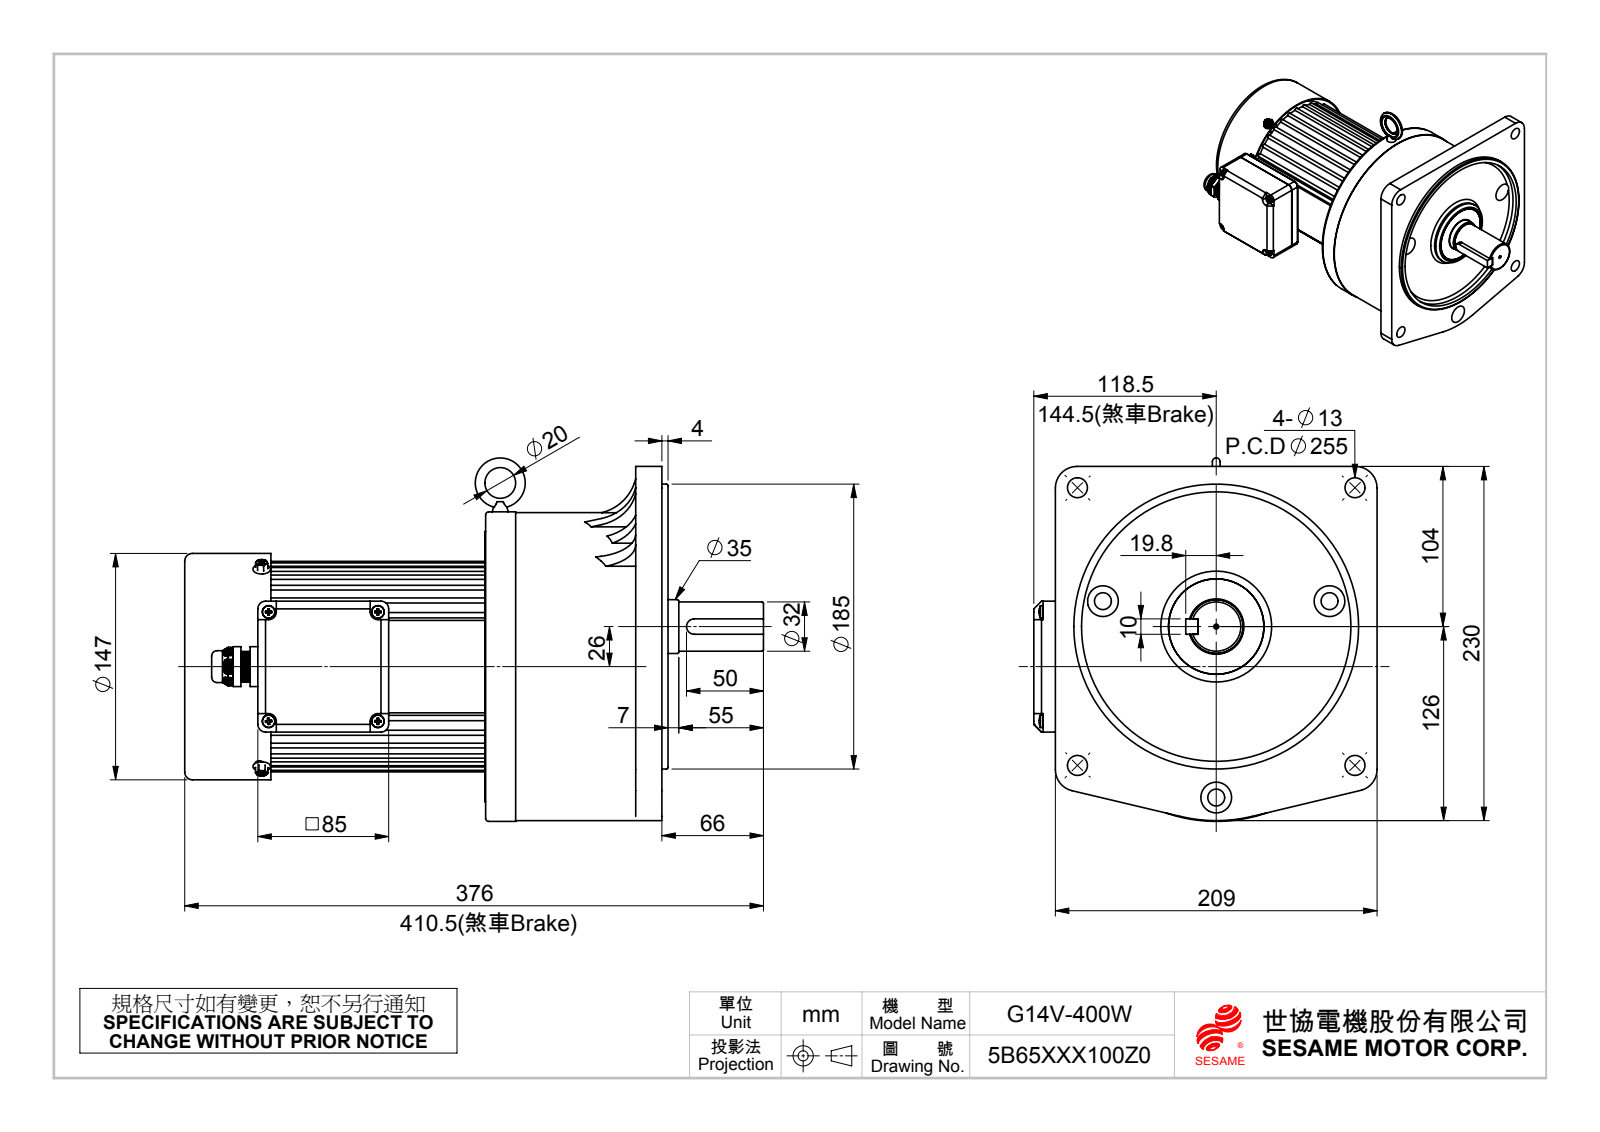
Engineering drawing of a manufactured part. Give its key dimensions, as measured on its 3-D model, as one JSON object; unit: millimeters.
{"part_name": "(標準品)G14V400W(5B65XXX100)(減速比共用); 出線盒下蓋; G14-400C1-03; 油封35x62x8 (+8 more)", "step_written_by": "SolidWorks 2010 (CONFIG_CONTROL_DESIGN)", "units": "millimeters", "bodies": {"solids": 20, "faces": 2705, "planar": 842, "cylindrical": 840, "other": 1023}, "overall_size": [376, 236, 223], "volume_mm3": 6473000, "surface_area_mm2": 567660, "round_holes": [[5, 14], [3.3, 9], [6, 5], [8, 4], [13, 4], [20, 4], [11, 3], [15, 3], [2, 1], [6.8, 1], [10.8, 1], [16.5, 1]], "round_bosses_or_shafts": [[8.3, 4], [4, 4], [5, 2], [201, 1], [200, 1], [185, 1], [175.47, 1], [147, 1]], "partial_cylinders_radius": [[1.85, 31], [1, 26], [0.5, 24], [3, 18], [5, 9], [30, 7], [2.75, 6], [14, 6]], "face_to_face_distances": [4, 25, 2, 115, 90, 111, 86, 165, 140, 251], "hole_center_spacings": [45, 71, 127.51, 180.32, 63.67, 85, 147.22, 11]}
